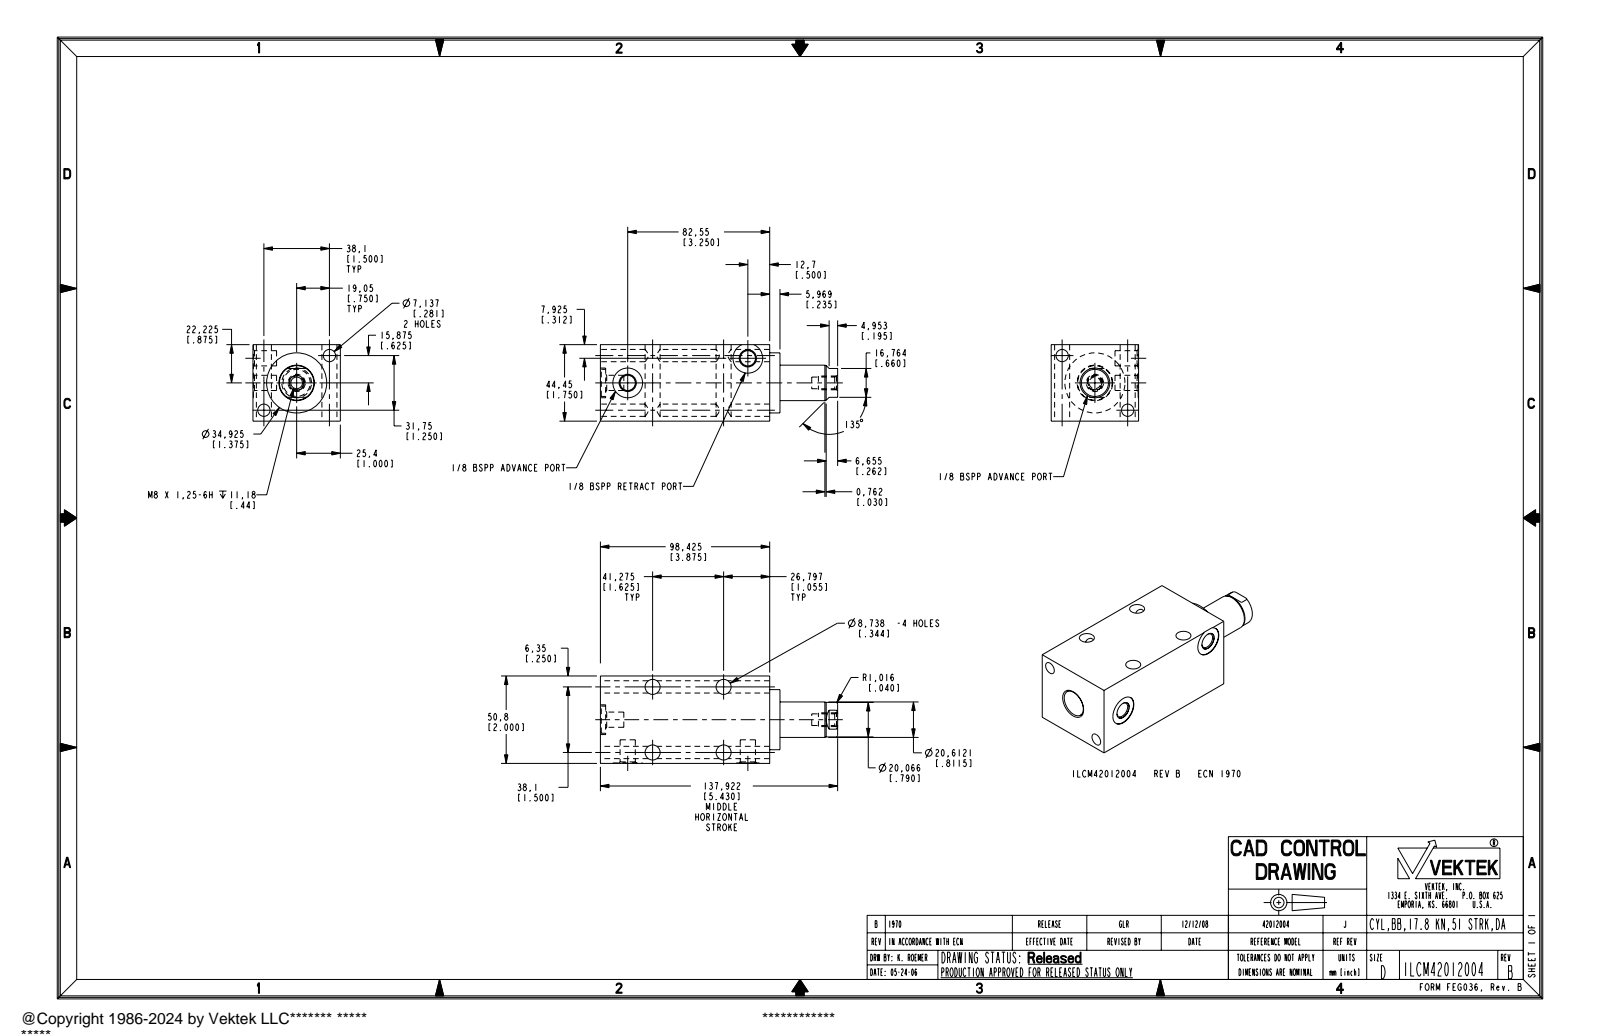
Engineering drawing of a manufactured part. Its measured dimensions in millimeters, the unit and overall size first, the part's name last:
Units: millimetres
Overall size (bounding box): 137.92 × 50.8 × 44.45
Round holes (diameter × count): ⌀8.74 ×4, ⌀8.84 ×3, ⌀10.03 ×3, ⌀17.27 ×3, ⌀7.14 ×2, ⌀6.78 ×1
Round bosses / shafts (diameter × count): ⌀34.92 ×1, ⌀20.61 ×1, ⌀20.07 ×1, ⌀15.75 ×1, ⌀8 ×1
Main face-to-face distances: 44.46, 50.8, 98.42, 5.97, 104.39, 50.55, 103.89, 97.92, 0.5, 33.53
Hole centre spacings: 24.8, 38.1, 41.27, 56.17, 49.6, 71.3
Volume: 218 398 mm³ · Surface area: 35 767 mm²
Bodies: 1 solid, 83 faces (22 planar, 49 cylindrical, 12 other)
Part name (STEP PRODUCT): ILCM42012004
STEP written by: PRO/ENGINEER BY PARAMETRIC TECHNOLOGY CORPORATION, 2007460 (AUTOMOTIVE_DESIGN_CC2)
